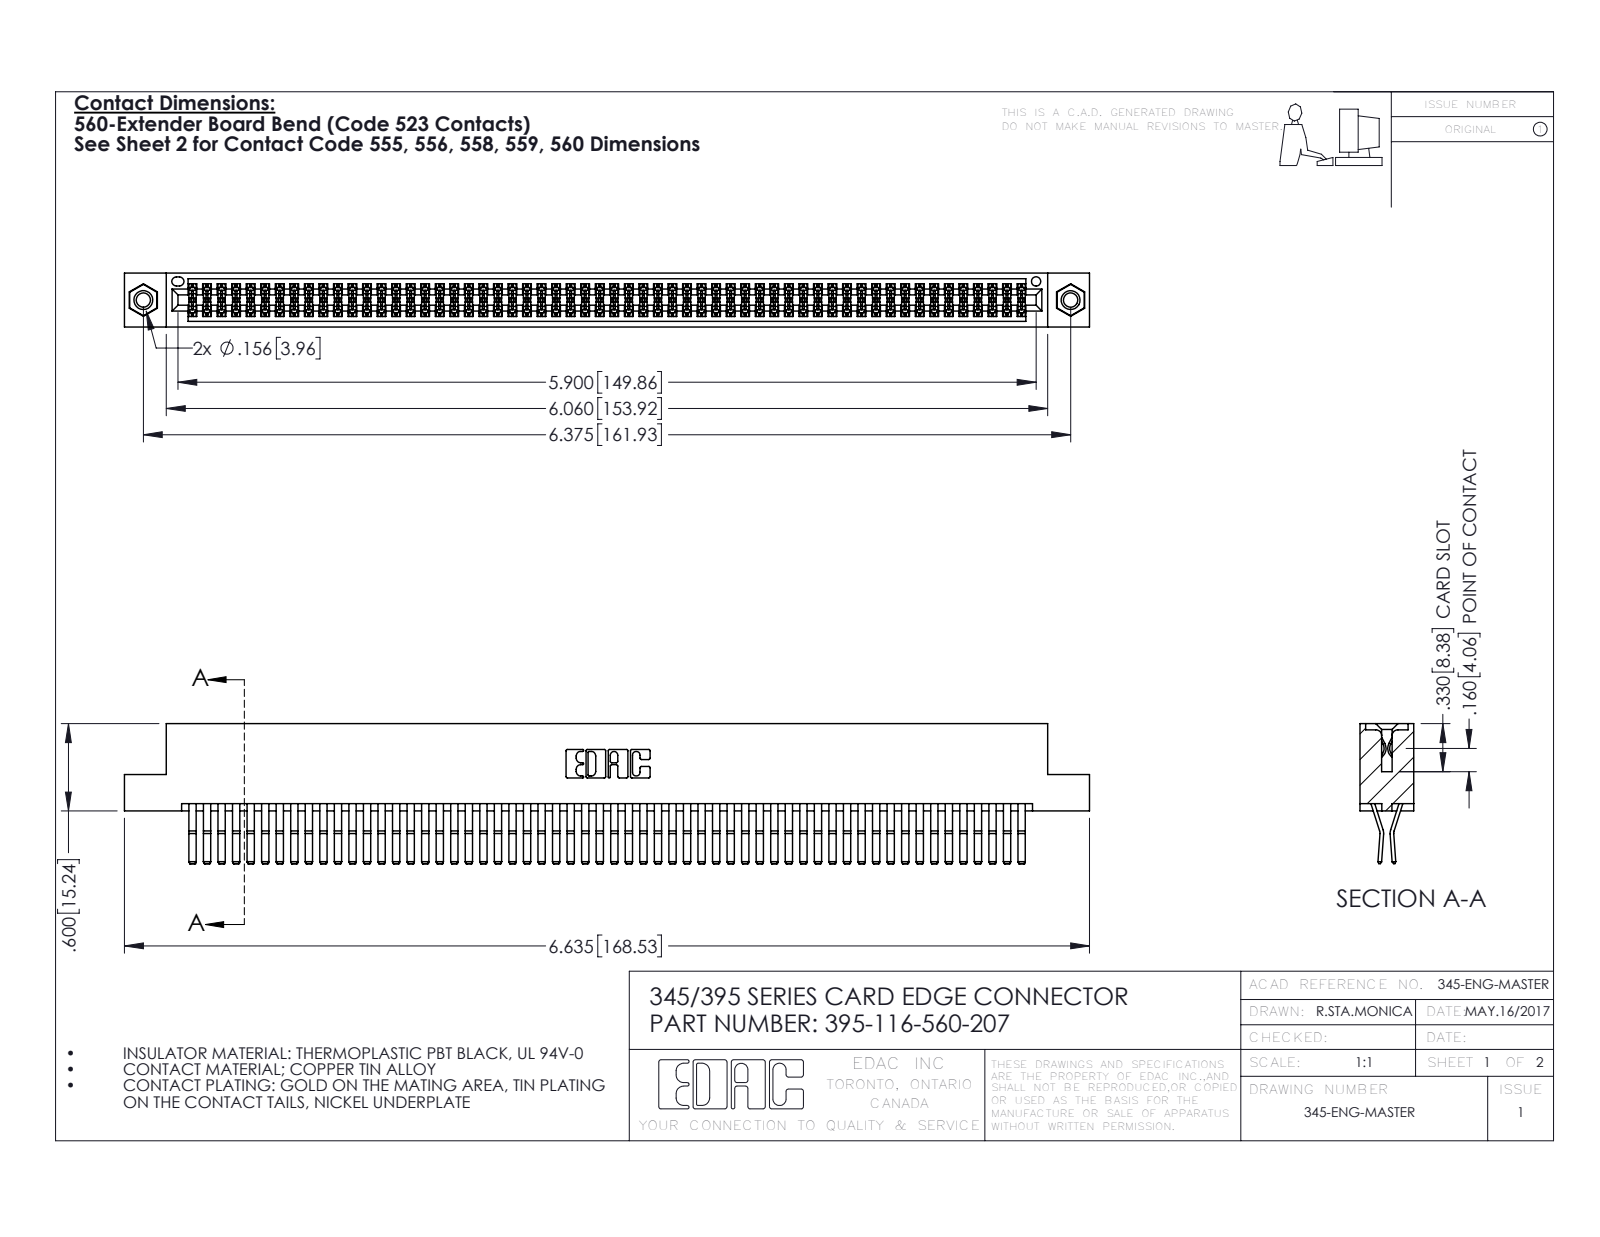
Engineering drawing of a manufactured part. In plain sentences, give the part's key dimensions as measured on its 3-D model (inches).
The part is named "345-292-001_560 Tail; 345-250-001_345-250-005-103; 345 Part_Flush Mounting Lugs - 0.156 Dia-TI; 395-116-560-207". Its 3-D file was written by "SolidWorks 2016 (CONFIG_CONTROL_DESIGN)". It is 119 solids with 6218 faces: 3940 planar, 2262 cylindrical and 16 other. Overall it measures 6.635 by 0.962 by 0.37 inches. Its volume is 1.054 cubic inches and its surface area 43.11 square inches. Round holes: 2 of diameter 0.098, 2 of diameter 0.125, 2 of diameter 0.156, 1 of diameter 0.064. Round bosses or shafts: 2 of diameter 0.155. Partial cylindrical surfaces (rounded edges, fillets, slot ends): 175 of radius 0.006, 22 of radius 0.01, 6 of radius 0.007, 6 of radius 0.031, 3 of radius 0.026, 2 of radius 0.01, 2 of radius 0.014, 2 of radius 0.019. The main face-to-face distances are 0.025, 0.072, 0.298, 0.37, 0.2, 0.098, 0.272, 0.225, 0.175, 0.149. The hole center spacings are 0.27, 6.139, 6.375.
